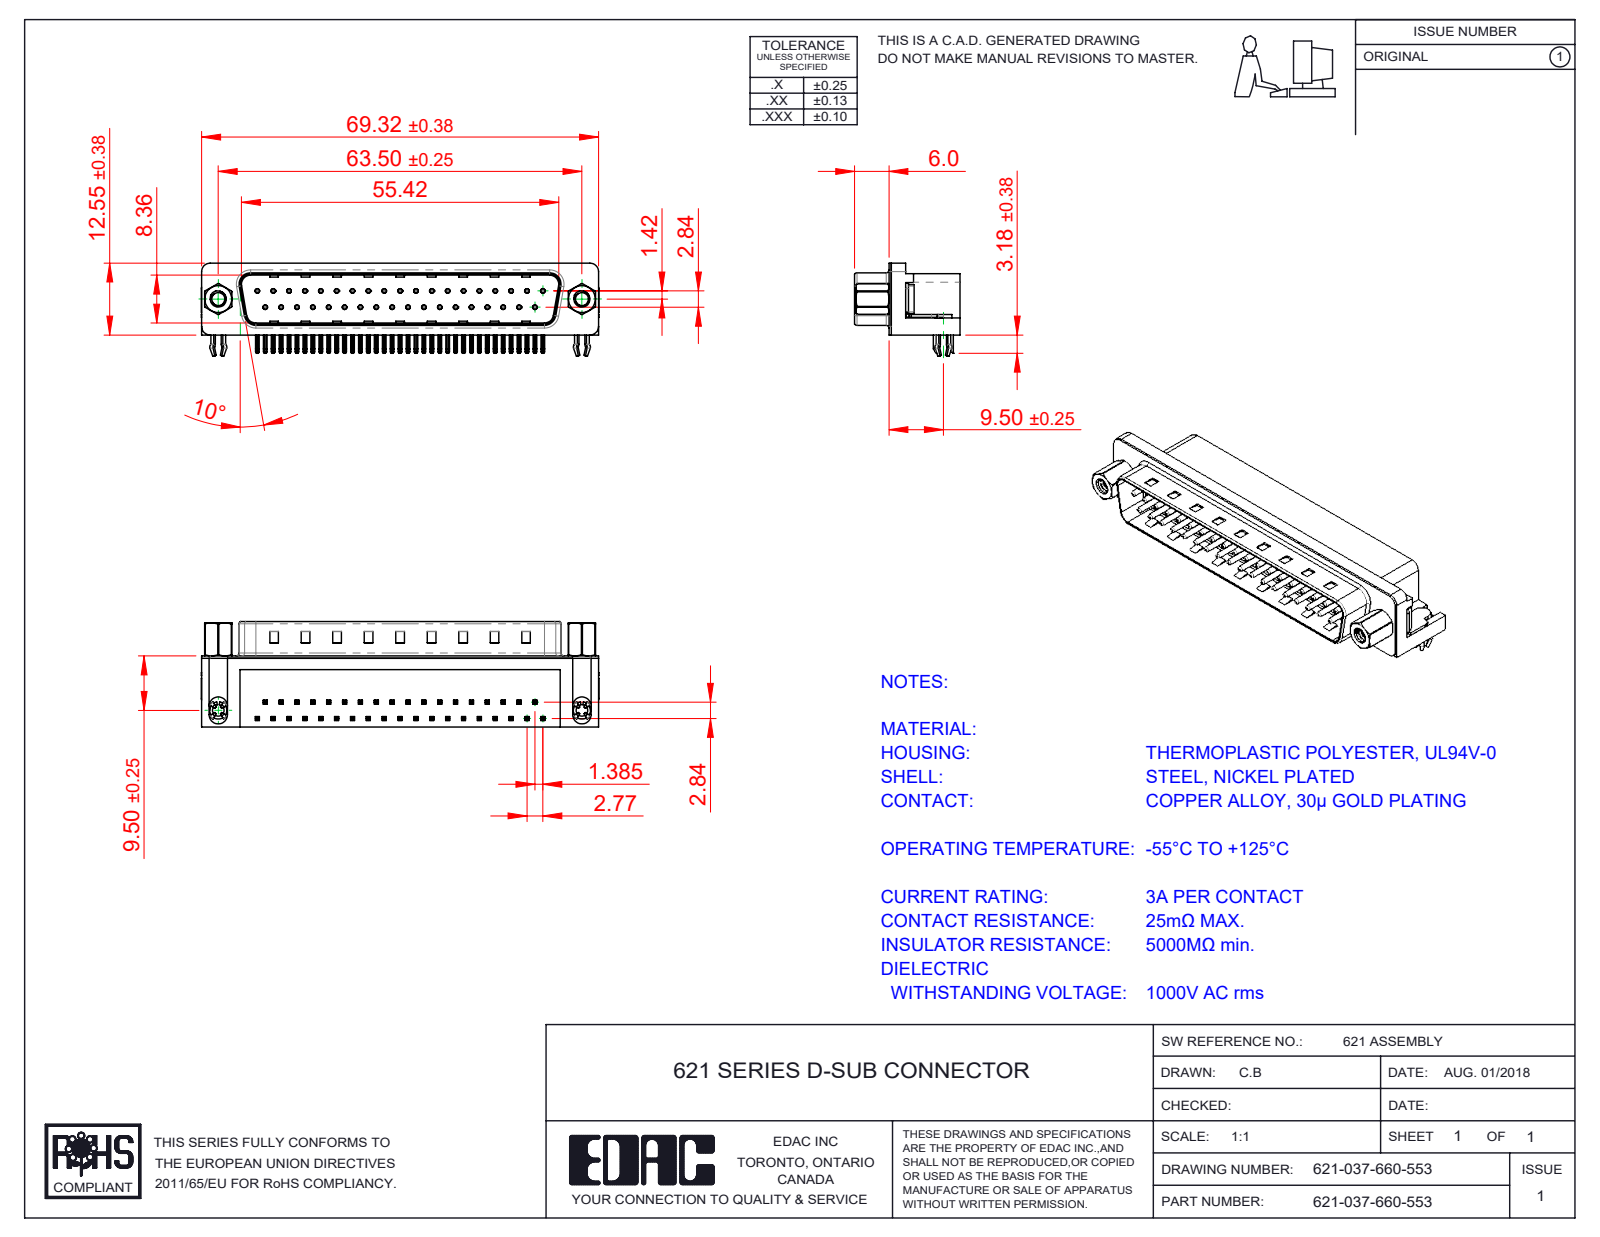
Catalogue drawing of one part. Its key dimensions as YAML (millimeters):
part_name: "621-037-660-553; 621 4-40 Hex Standoff 5; 621 4-40 Threaded Board Mount; 621 4-40 Threaded Rivet (+4 more)"
step_written_by: "SolidWorks 2016 (CONFIG_CONTROL_DESIGN)"
units: millimeters
bodies: {solids: 45, faces: 3355, planar: 2035, cylindrical: 999, other: 321}
overall_size: [69.4, 18.4, 15.73]
volume: 8846
surface_area: 10656
round_holes:
  - {diameter: 0.35, count: 37}
  - {diameter: 0.8, count: 37}
  - {diameter: 2.26, count: 4}
  - {diameter: 2.29, count: 2}
  - {diameter: 4, count: 2}
  - {diameter: 4.8, count: 2}
  - {diameter: 5, count: 2}
round_bosses_or_shafts:
  - {diameter: 0.75, count: 37}
  - {diameter: 4.9, count: 2}
  - {diameter: 4.75, count: 2}
  - {diameter: 3.9, count: 2}
  - {diameter: 3.26, count: 2}
  - {diameter: 2.79, count: 2}
partial_cylinders:
  - {radius: 0.25, count: 156}
  - {radius: 0.12, count: 74}
  - {radius: 1, count: 16}
  - {radius: 0.5, count: 9}
  - {radius: 1.6, count: 8}
  - {radius: 1.5, count: 7}
  - {radius: 0.9, count: 4}
  - {radius: 2, count: 4}
face_to_face_distances: [0.4, 12, 10.35, 8.76, 2.1, 1.7, 10.46, 10.86, 12.4, 9]
hole_center_spacings: [3.16, 2.77, 5.54, 8.31, 11.08, 13.85, 19.39, 22.16]
